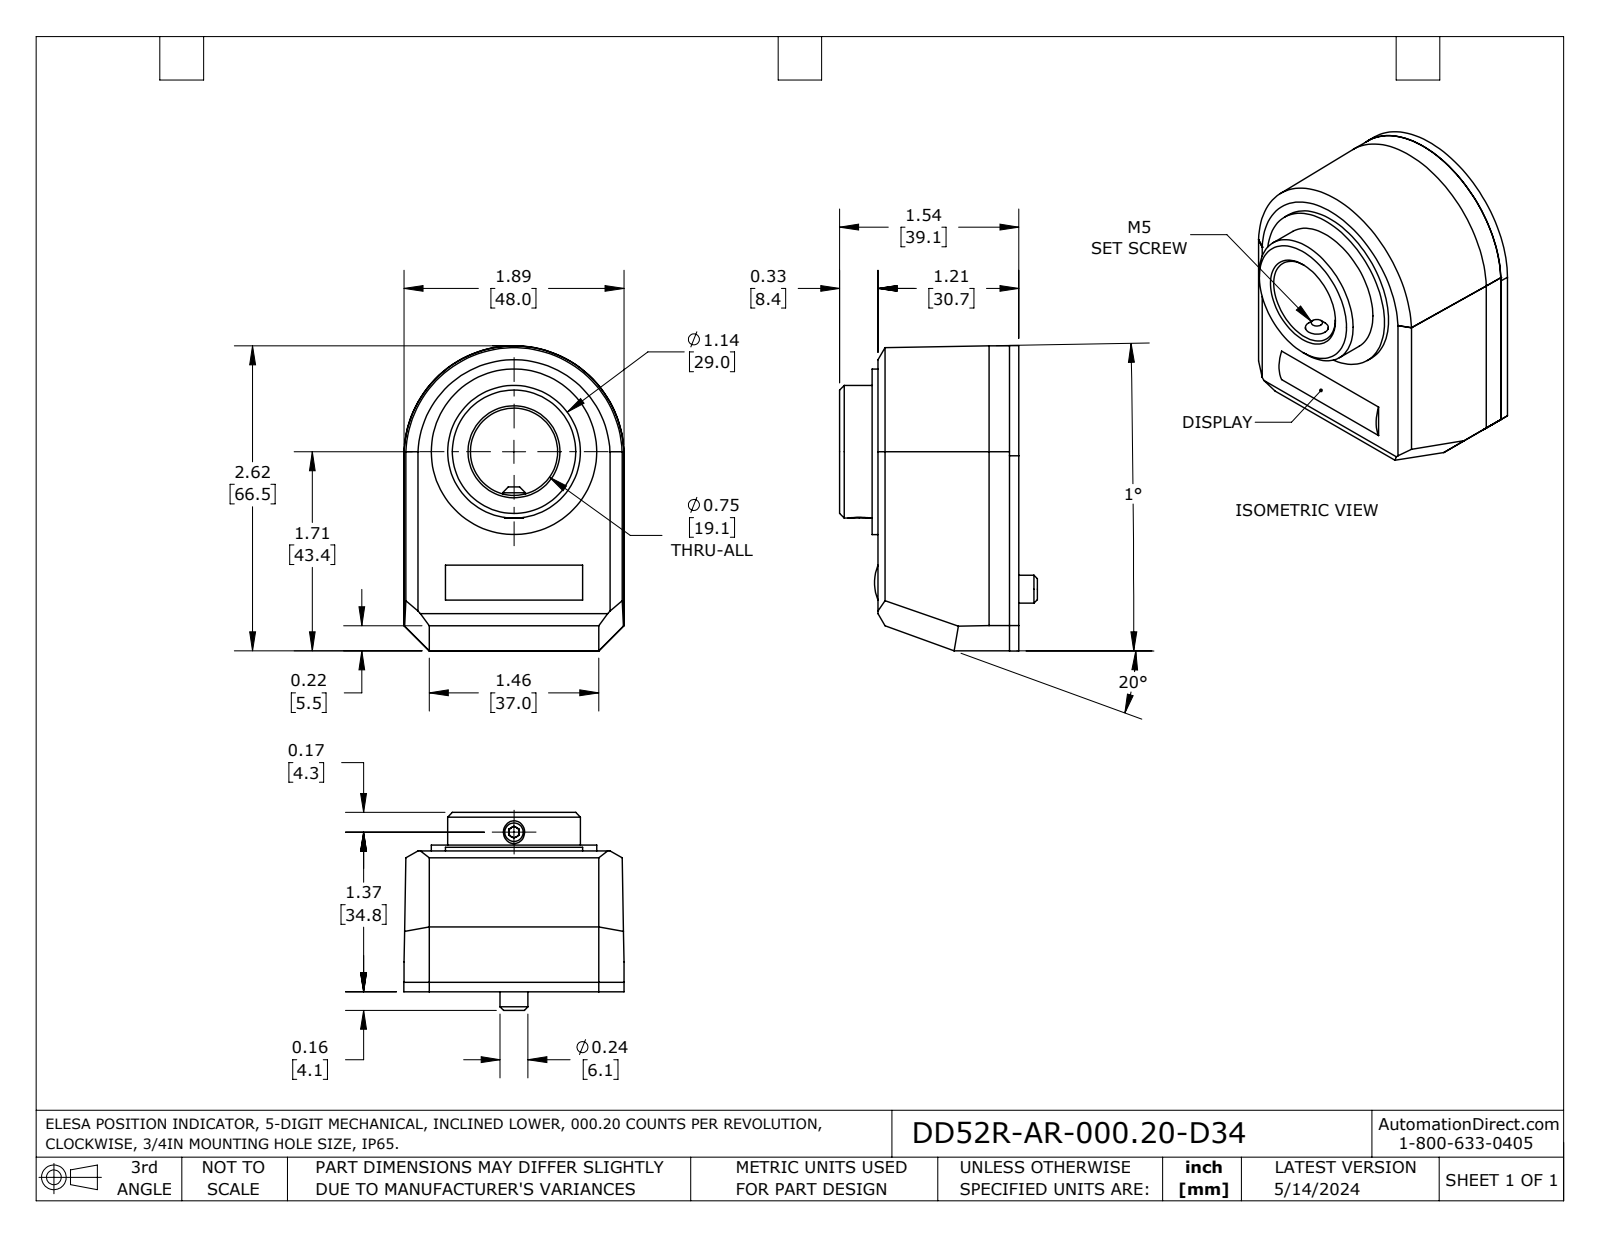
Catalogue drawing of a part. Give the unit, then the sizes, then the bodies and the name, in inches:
Units: inches
Overall size (bounding box): 2.622 × 1.892 × 1.7
Round holes (diameter × count): ⌀0.163 ×1, ⌀0.75 ×1, ⌀0.945 ×1, ⌀1.57 ×1, ⌀1.58 ×1
Round bosses / shafts (diameter × count): ⌀1.422 ×1, ⌀1.14 ×1, ⌀0.24 ×1, ⌀0.197 ×1
Partial cylindrical surfaces — rounded edges, fillets, slot ends (radius × count): R0.39 ×1, R0.945 ×1, R0.946 ×1
Main face-to-face distances: 1.21, 1.051, 0.159, 0.05, 1.101, 1.26, 0.28, 0.33, 1.381, 1.54
Volume: 4.683 in³ · Surface area: 28.91 in²
Bodies: 3 solids, 68 faces (46 planar, 13 cylindrical, 9 other)
Part name (STEP PRODUCT): DD52R-AR-INCH
STEP written by: SolidWorks 2023 (AUTOMOTIVE_DESIGN)
